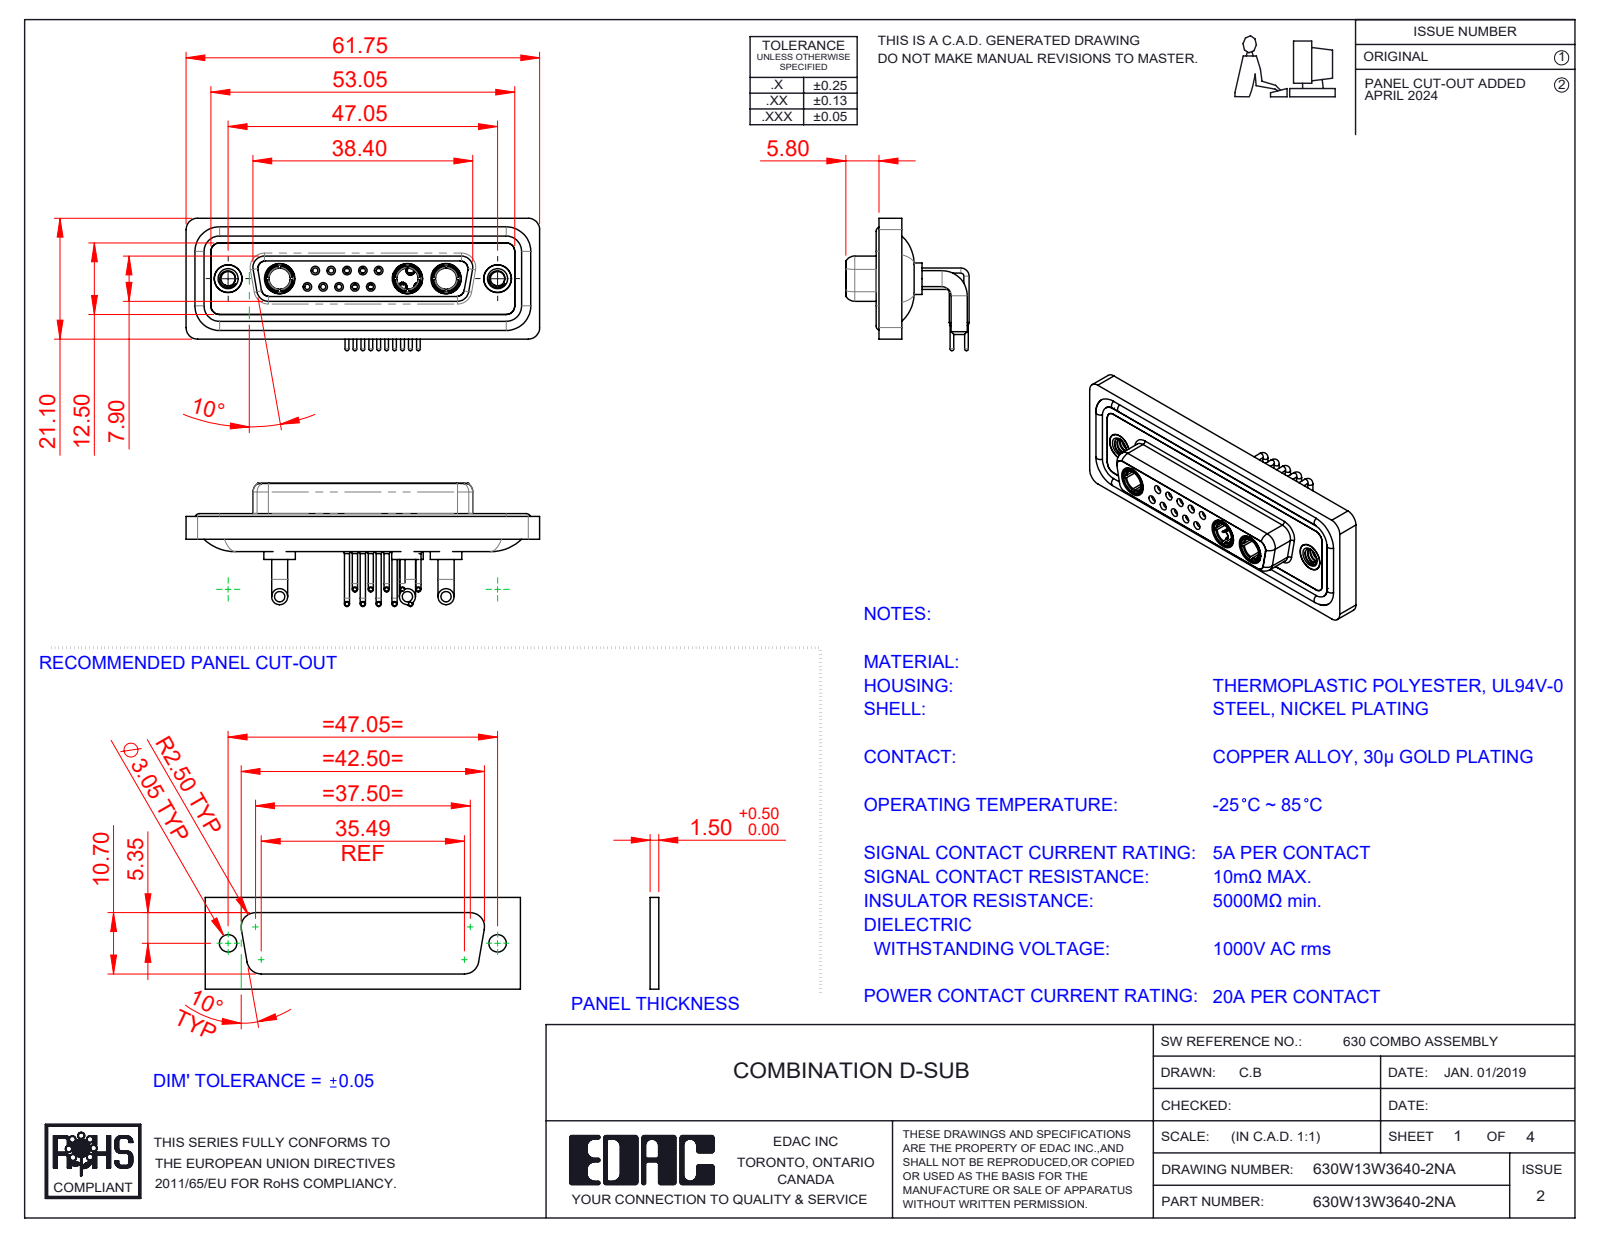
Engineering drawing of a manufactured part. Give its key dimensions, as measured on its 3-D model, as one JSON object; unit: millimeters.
{"part_name": "Power Socket_20A RA; 630Combo Contact Row 2_50 Contacts; 630Combo Housing_13W3; 630Combo Threaded Rivet_A (+5 more)", "step_written_by": "SolidWorks 2023 (CONFIG_CONTROL_DESIGN)", "units": "millimeters", "bodies": {"solids": 23, "faces": 1144, "planar": 342, "cylindrical": 491, "other": 311}, "overall_size": [61.75, 23.12, 21.53], "volume_mm3": 8463, "surface_area_mm2": 14299, "round_holes": [[0.9, 10], [1.1, 10], [1.5, 10], [2, 10], [1.6, 5], [1.7, 5], [4.85, 5], [3.7, 3], [5.3, 3], [2.5, 2], [4, 2], [4.05, 2]], "round_bosses_or_shafts": [[0.9, 15], [1.6, 12], [0.65, 10], [2.8, 6], [2, 5], [1.5, 5], [5.5, 3], [5.2, 3]], "partial_cylinders_radius": [[1.5, 18], [2, 18], [1.35, 8], [1.6, 8], [0.25, 4], [0.5, 4], [0.6, 4], [0.65, 4]], "face_to_face_distances": [0.4, 1.8, 4.1, 1.1, 1.6, 1.5, 3.1, 2.5, 3.7, 1.4], "hole_center_spacings": [3.16, 2.77, 5.54, 5.04, 8.31, 5.03, 7.49, 11.08]}
